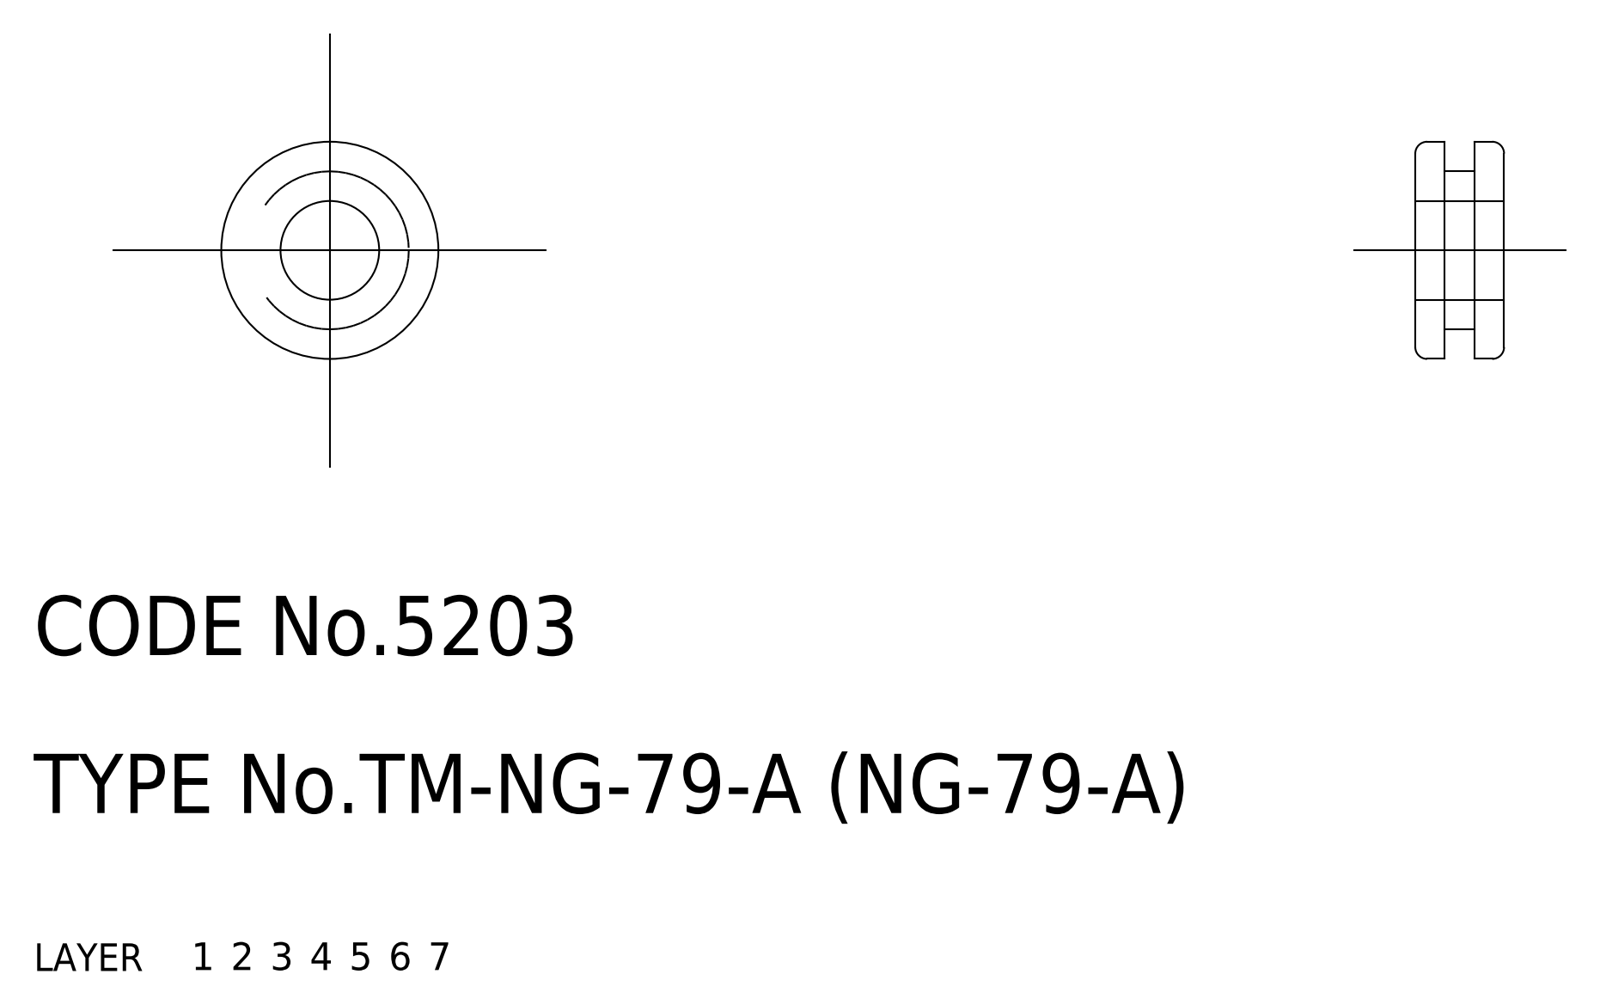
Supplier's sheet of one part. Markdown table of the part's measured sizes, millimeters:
| quantity | value |
| --- | --- |
| part name | grommet |
| STEP written by | CADfix (AUTOMOTIVE_DESIGN) |
| units | millimeters |
| bodies | 1 solid, 16 faces (0 planar, 0 cylindrical, 16 other) |
| overall size | 11 × 11 × 4.5 |
| volume | 268 mm³ |
| surface area | 434 mm² |
